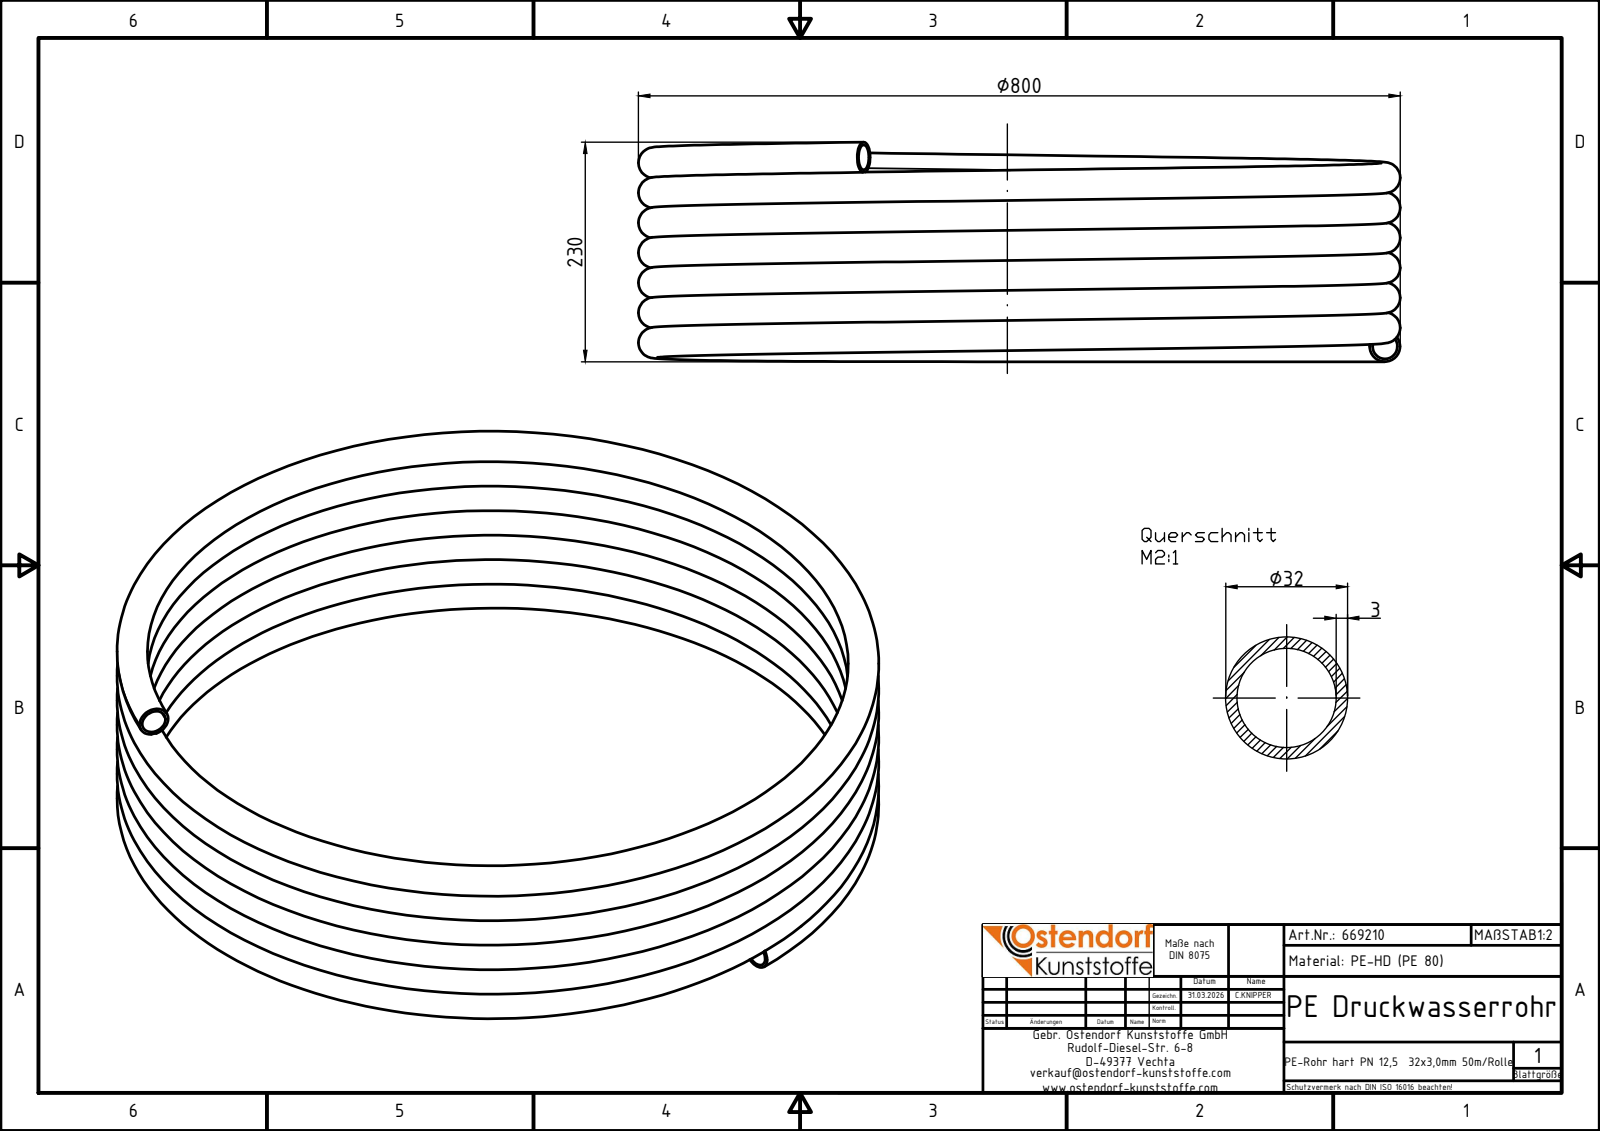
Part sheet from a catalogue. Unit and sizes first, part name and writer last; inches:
Units: inches
Overall size (bounding box): 31.496 × 31.496 × 9.079
Volume: 261.7 in³ · Surface area: 4 253 in²
Bodies: 1 solid, 7 faces (3 planar, 0 cylindrical, 4 other)
Part name (STEP PRODUCT): 669210z
STEP written by: Autodesk Inventor 2024 (AUTOMOTIVE_DESIGN)
